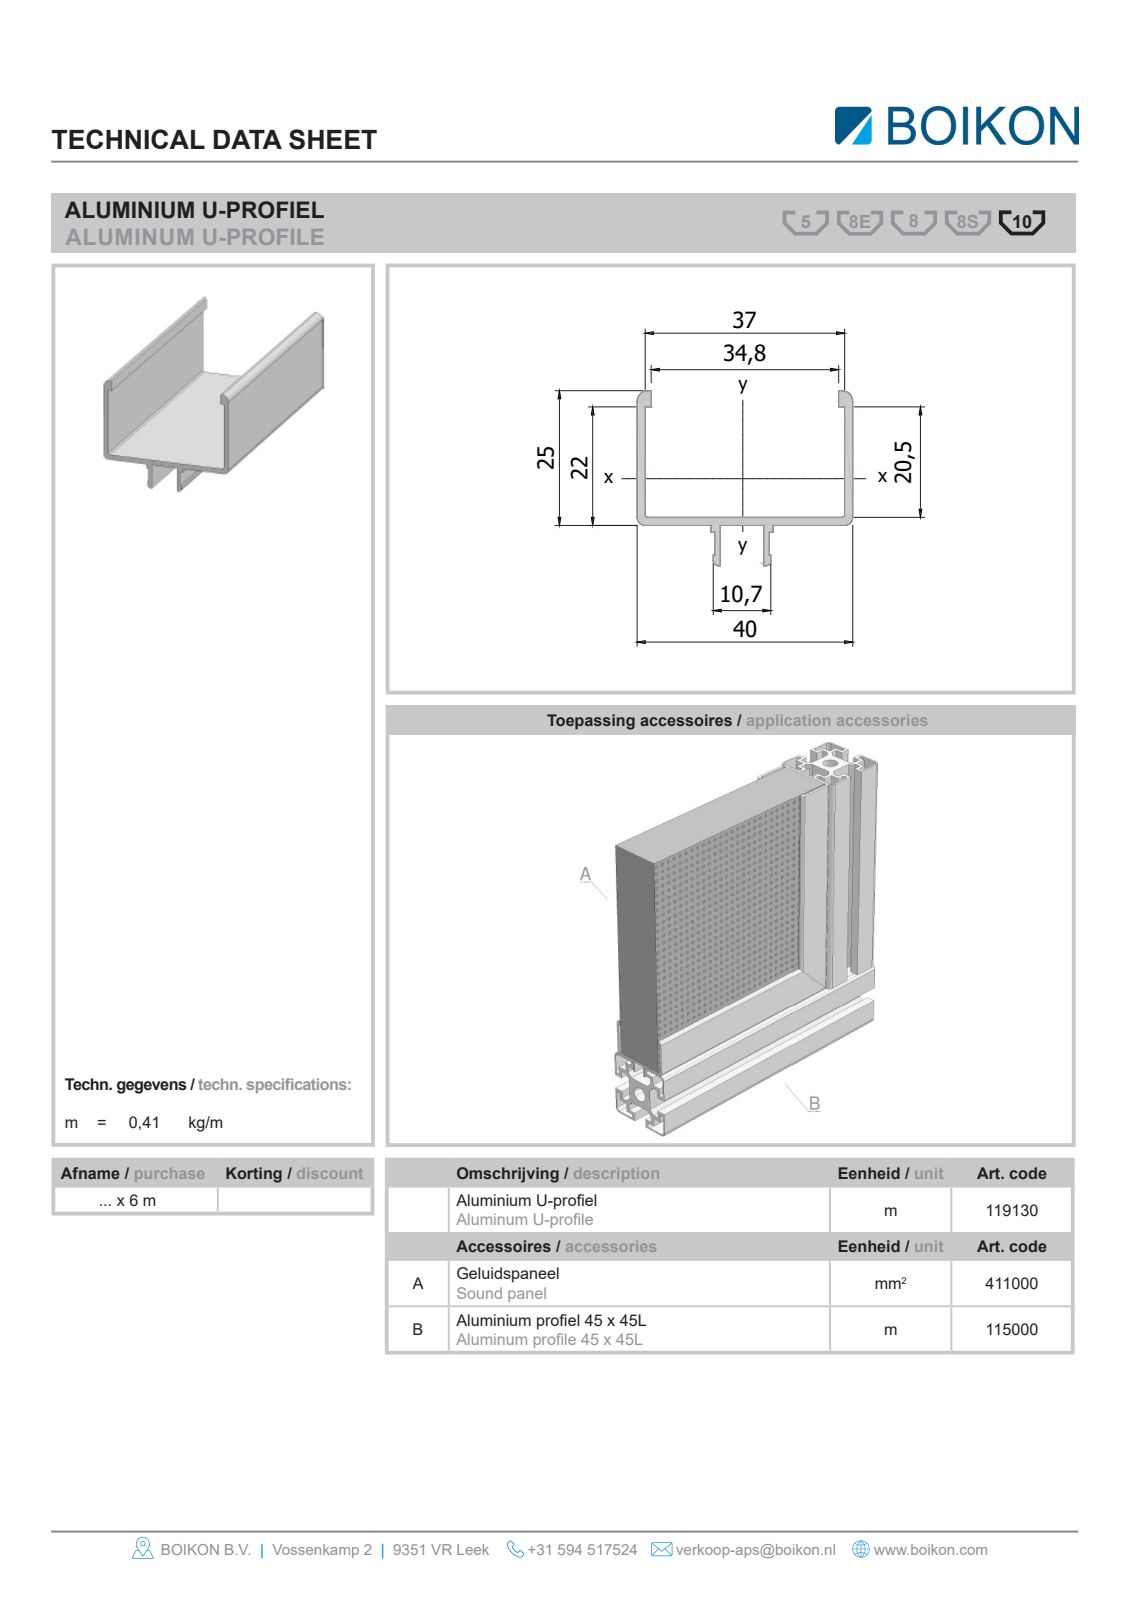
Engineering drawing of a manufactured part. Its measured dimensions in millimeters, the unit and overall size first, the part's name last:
Units: millimetres
Overall size (bounding box): 1000 × 40 × 32.5
Partial cylindrical surfaces — rounded edges, fillets, slot ends (radius × count): R0.5 ×2, R1 ×2, R1.5 ×2, R2 ×2
Main face-to-face distances: 1.5, 38.5, 40, 37, 1, 9.1, 15.41, 23.51, 13.91, 22.01
Volume: 152 046 mm³ · Surface area: 208 612 mm²
Bodies: 1 solid, 38 faces (30 planar, 8 cylindrical, 0 other)
Part name (STEP PRODUCT): Root; 119130U-profiel voor geluidspaneelBOIKON0
STEP written by: HiCAD 2013 1802.4 Build 509 (AUTOMOTIVE_DESIGN)
